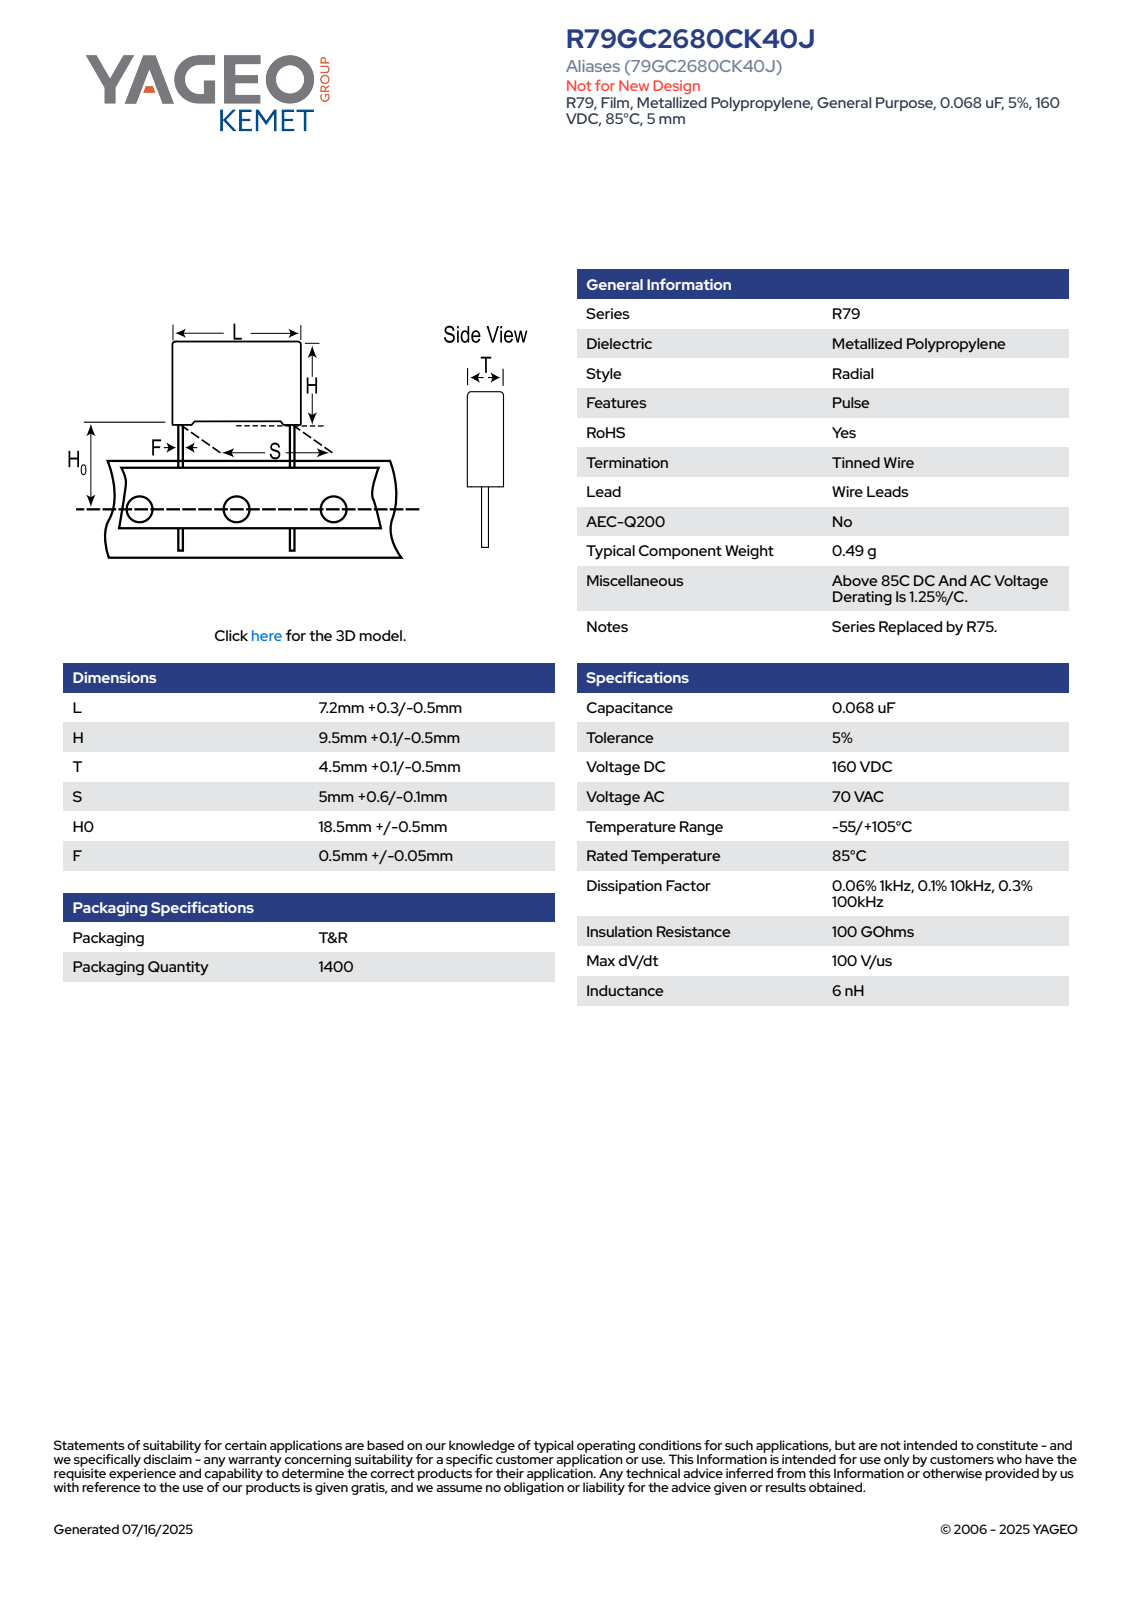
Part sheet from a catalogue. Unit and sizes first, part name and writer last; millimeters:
Units: millimetres
Overall size (bounding box): 28.6 × 7.5 × 4.61
Round bosses / shafts (diameter × count): ⌀0.55 ×2
Partial cylindrical surfaces — rounded edges, fillets, slot ends (radius × count): R0.5 ×4
Main face-to-face distances: 4.6, 7.5, 8.85, 4.35, 7.25, 0.75, 9.6, 4.1, 7, 0.33
Volume: 318 mm³ · Surface area: 383 mm²
Bodies: 4 solids, 85 faces (77 planar, 8 cylindrical, 0 other)
Part name (STEP PRODUCT): CFR_RB2_7.2X9.5X4.5_L7.5H9.6T4.6S5H019F0.55
STEP written by: SolidWorks 2020 (AUTOMOTIVE_DESIGN)
